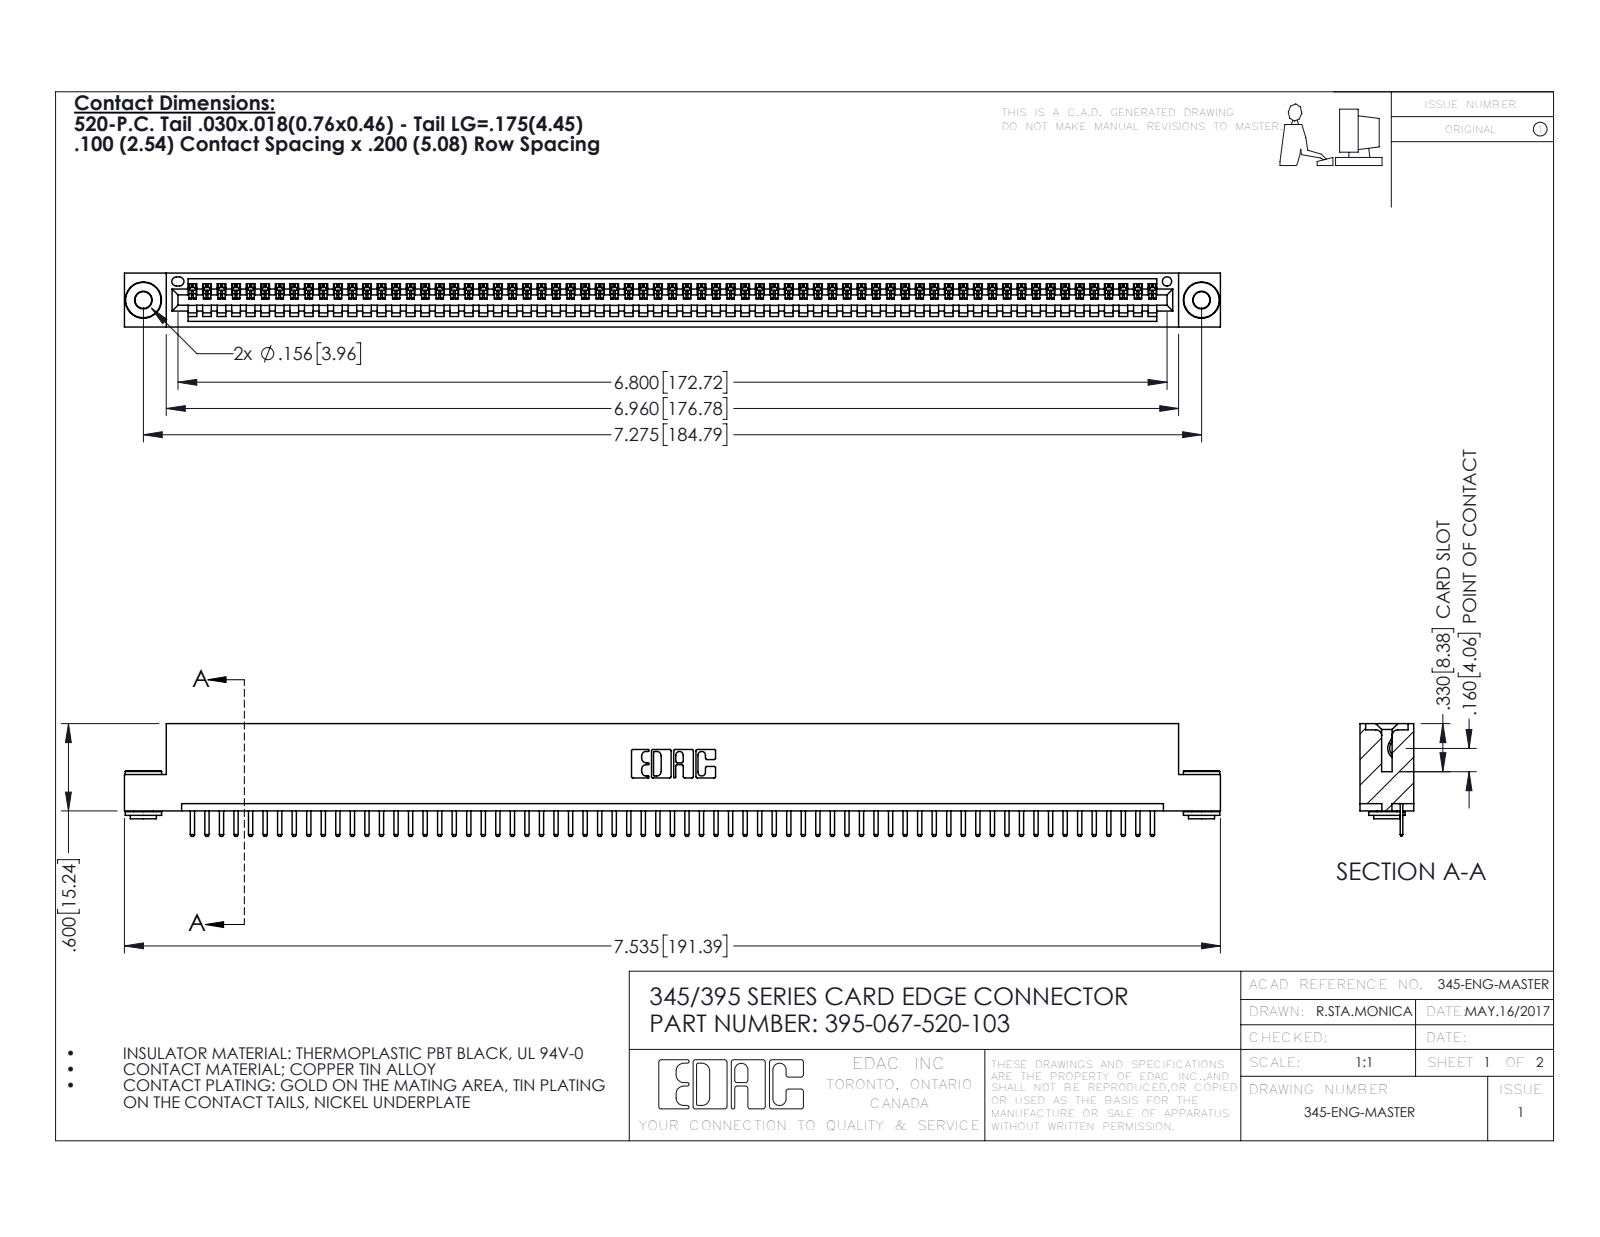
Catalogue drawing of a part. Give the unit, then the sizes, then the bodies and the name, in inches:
Units: inches
Overall size (bounding box): 7.535 × 0.775 × 0.37
Round holes (diameter × count): ⌀0.116 ×2, ⌀0.156 ×2, ⌀0.064 ×1
Round bosses / shafts (diameter × count): ⌀0.25 ×2, ⌀0.18 ×2, ⌀0.136 ×2
Partial cylindrical surfaces — rounded edges, fillets, slot ends (radius × count): R0.01 ×136, R0.006 ×134, R0.01 ×22, R0.007 ×6, R0.031 ×6, R0.026 ×3, R0.031 ×2, R0.04 ×2
Main face-to-face distances: 0.072, 0.298, 0.37, 0.2, 0.025, 0.098, 0.272, 0.225, 0.072, 0.149
Hole centre spacings: 0.27, 7.039, 7.275
Volume: 1.111 in³ · Surface area: 37.39 in²
Bodies: 70 solids, 4318 faces (2904 planar, 1406 cylindrical, 8 other)
Part name (STEP PRODUCT): 345 Part_Flush Mounting Lugs - 0.156 Dia-TH; 395-067-520-103; 345-250-002_345-250-002-102; 345-292-001_345-293-120
STEP written by: SolidWorks 2016 (CONFIG_CONTROL_DESIGN)
